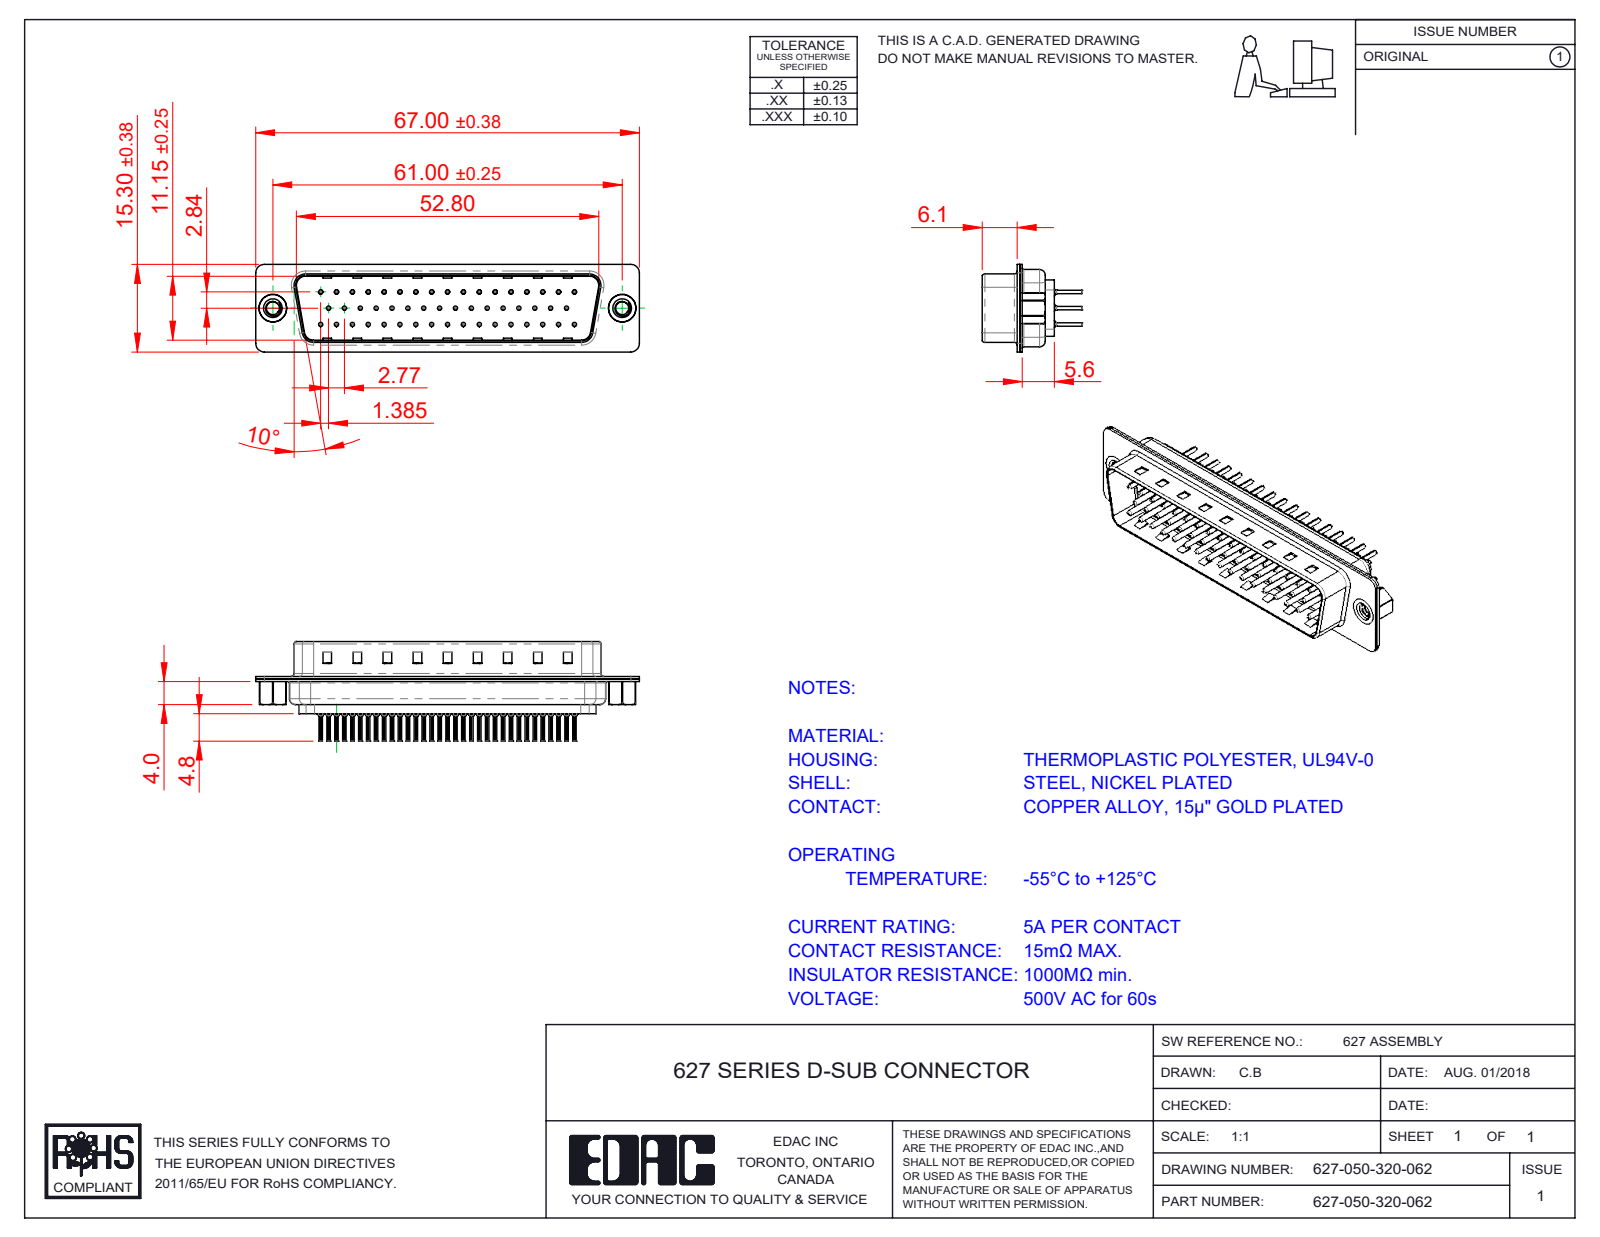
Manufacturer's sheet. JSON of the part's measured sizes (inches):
{"part_name": "627 Contact Row 3_20L; 627 Shell Rear_50 Contacts; 627 Contact Row 2_20L; 627 Housing_50 LP (+4 more)", "step_written_by": "SolidWorks 2020 (CONFIG_CONTROL_DESIGN)", "units": "inches", "bodies": {"solids": 55, "faces": 5308, "planar": 1403, "cylindrical": 1989, "other": 1916}, "overall_size": [2.638, 0.681, 0.602], "volume_in3": 0.27, "surface_area_in2": 19.49, "round_holes": [[0.008, 50], [0.014, 50], [0.043, 50], [0.063, 50], [0.089, 2], [0.157, 2], [0.189, 2]], "round_bosses_or_shafts": [[0.079, 50], [0.059, 50], [0.03, 50], [0.024, 50], [0.197, 2], [0.193, 2]], "partial_cylinders_radius": [[0.004, 100], [0.059, 16], [0.079, 12], [0.02, 8], [0.063, 8], [0.01, 4], [0.024, 4], [0.026, 4]], "face_to_face_distances": [0.016, 0.018, 0.455, 0.035, 0.238, 0.256, 0.031, 0.485, 0.077, 0.03], "hole_center_spacings": [0.124, 0.109, 0.218, 0.327, 0.436, 0.545, 0.654, 0.198]}
